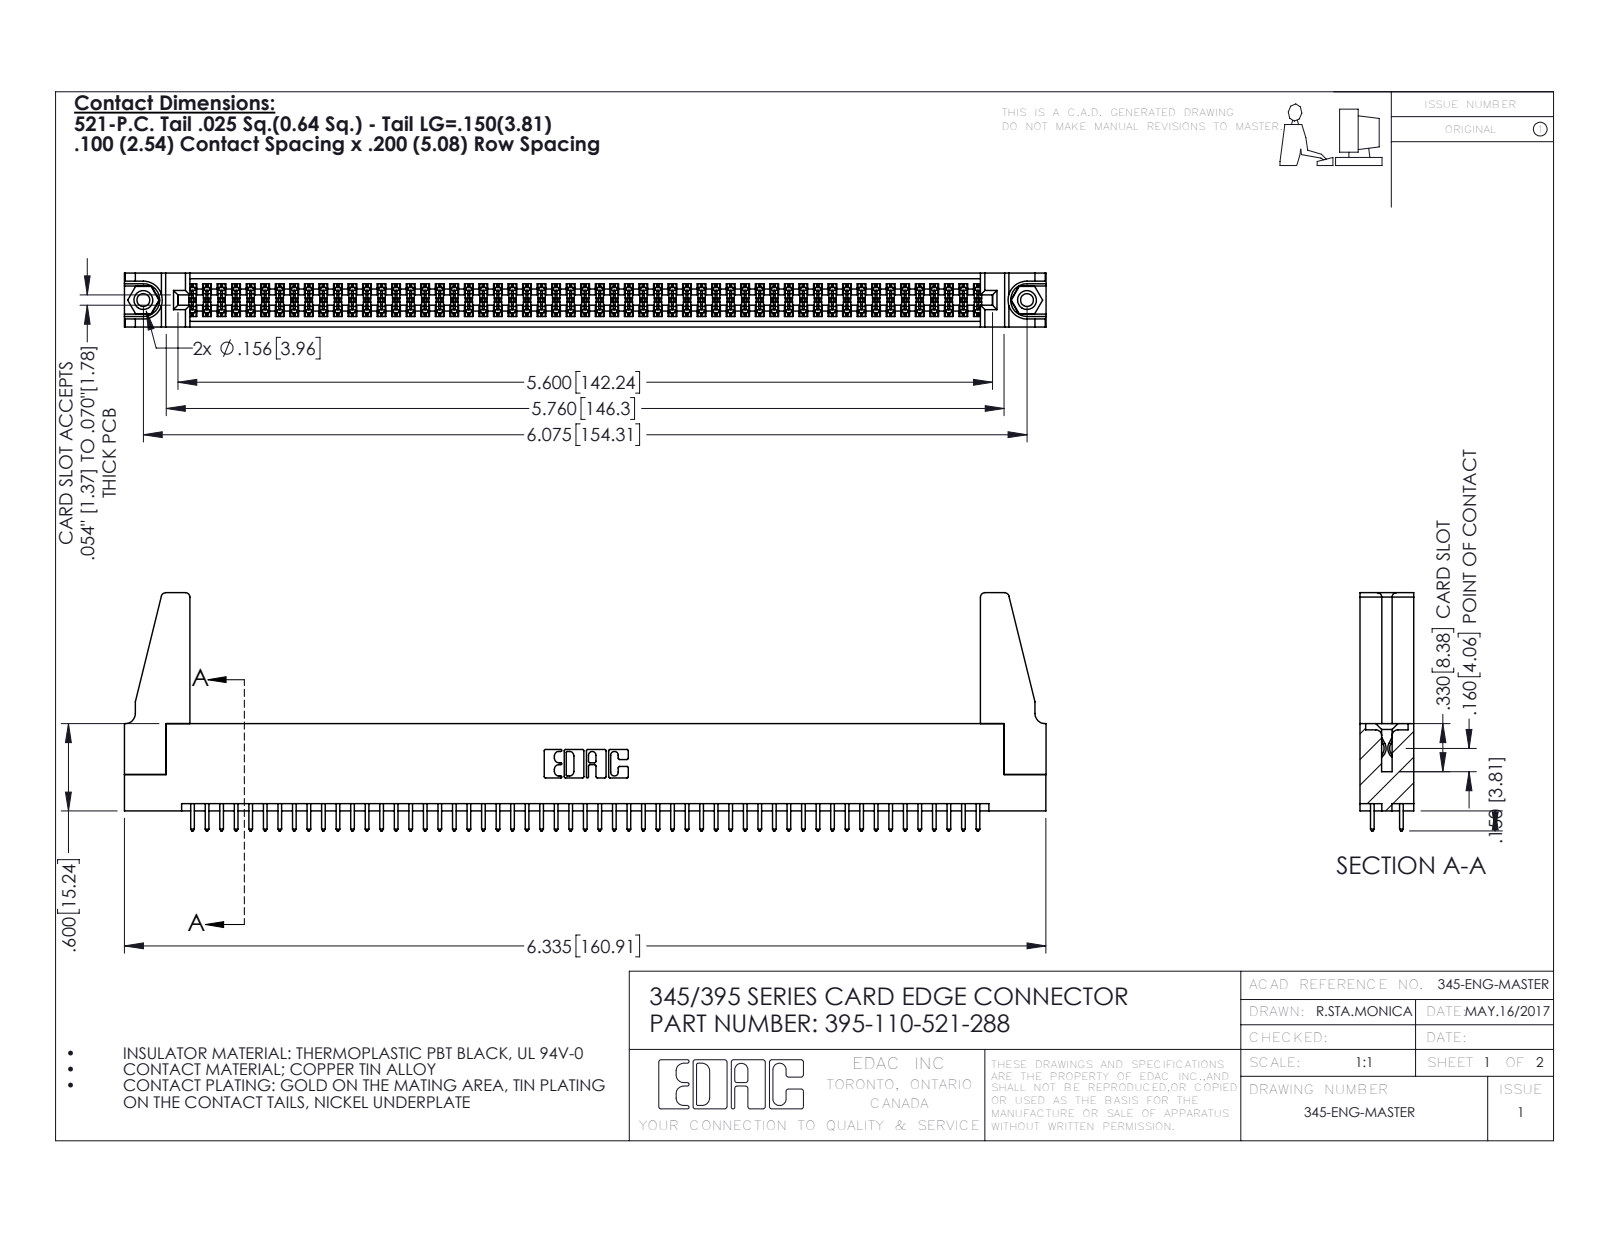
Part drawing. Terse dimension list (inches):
name: 345 Part_Flush Mounting Lugs - 0.156 Dia-TH; 345-292-001_345-293-121; 345-220-078_345-220-088; 395-110-521-288 (+1 more)
written by: SolidWorks 2016 (CONFIG_CONTROL_DESIGN)
unit: in
bodies: 115 solids, 5750 faces (3782 planar, 1952 cylindrical, 16 other)
size: 6.336 × 1.637 × 0.37
volume: 1.157 in³; area: 40.77 in²
holes: 2× ⌀0.089, 2× ⌀0.125, 2× ⌀0.156, 1× ⌀0.064
bosses: 2× ⌀0.155
rounds: 165× R0.006, 110× R0.01, 22× R0.01, 8× R0.03, 6× R0.007, 6× R0.031, 3× R0.026, 2× R0.014
face distances: 0.072, 0.298, 0.37, 0.2, 0.098, 0.272, 0.025, 0.225, 0.175, 0.149
hole spacings: 0.27, 5.839, 6.075
